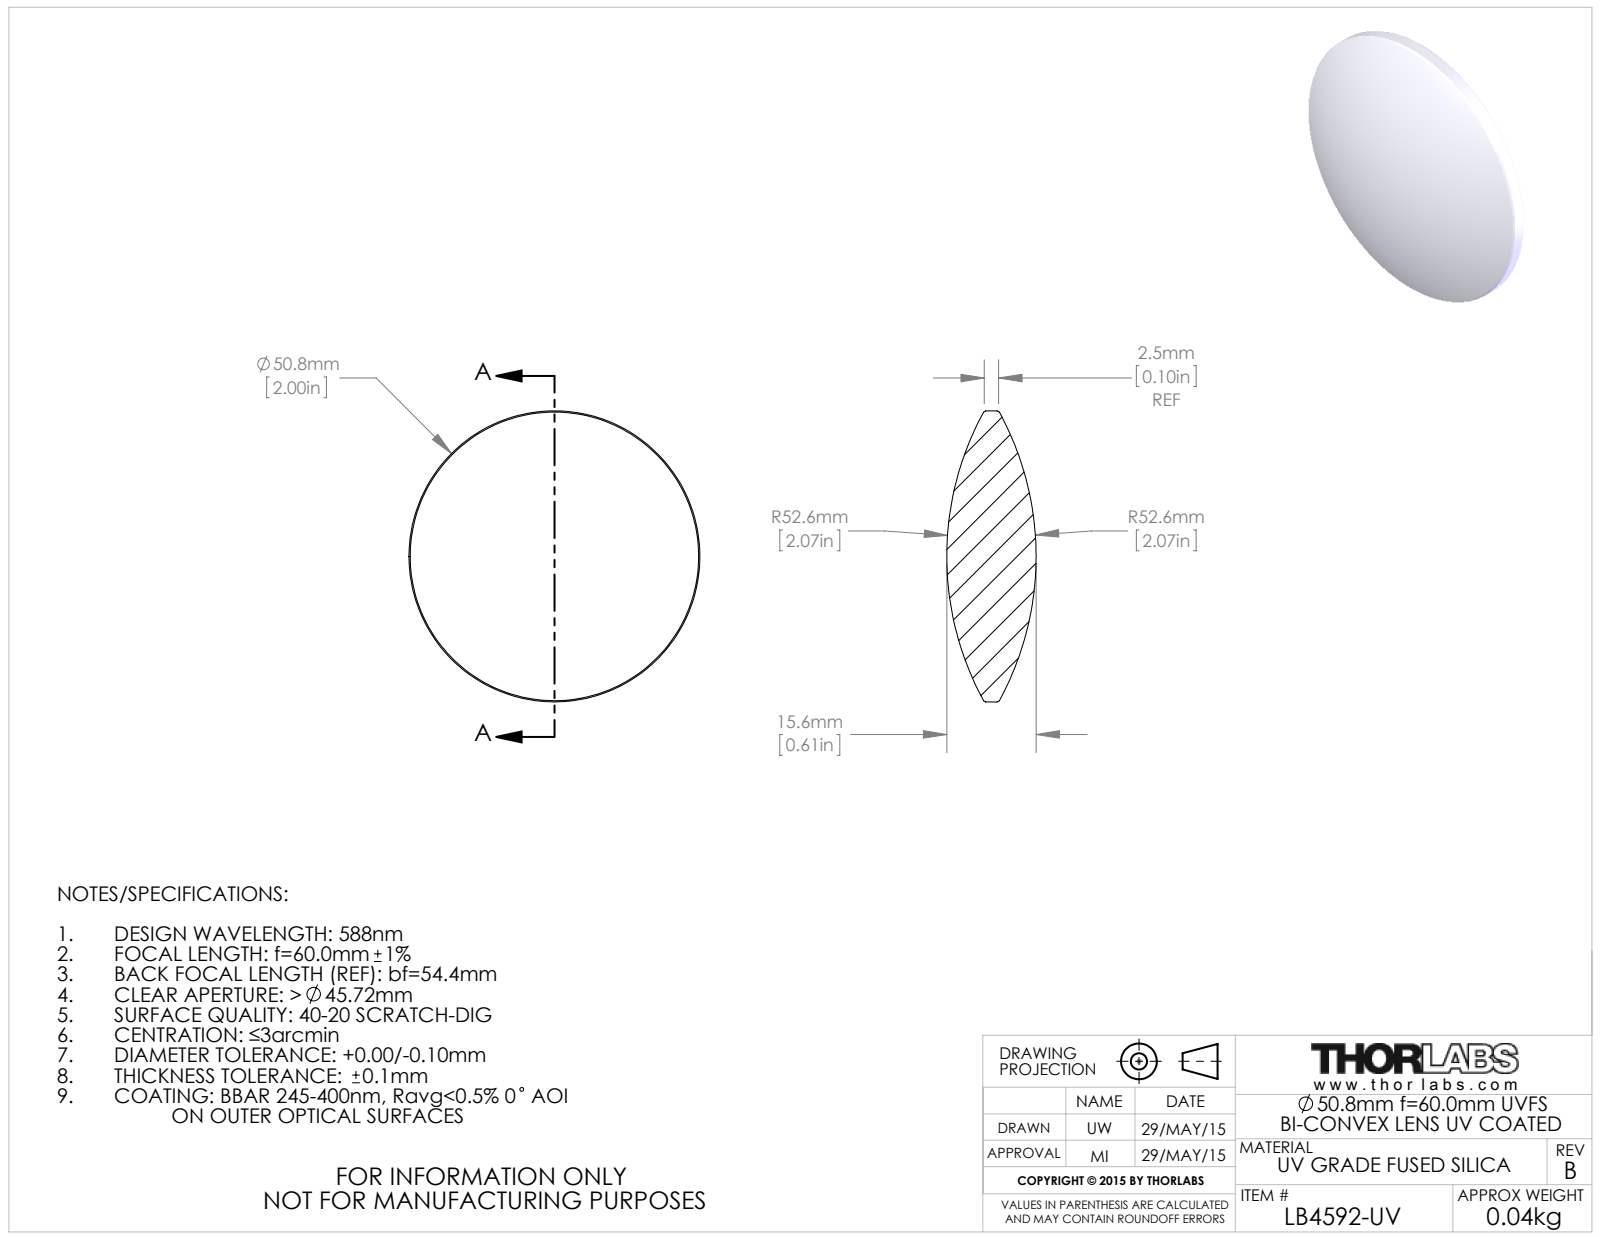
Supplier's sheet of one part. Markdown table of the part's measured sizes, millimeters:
| quantity | value |
| --- | --- |
| part name | 4331-E0W |
| STEP written by | SolidWorks 2014 (CONFIG_CONTROL_DESIGN) |
| units | millimeters |
| bodies | 1 solid, 10 faces (0 planar, 2 cylindrical, 8 other) |
| overall size | 50.8 × 50.8 × 15.6 |
| volume | 18 649 mm³ |
| surface area | 4 702 mm² |
| round bosses / shafts (diameter × count) | 50.8 × 1 |
